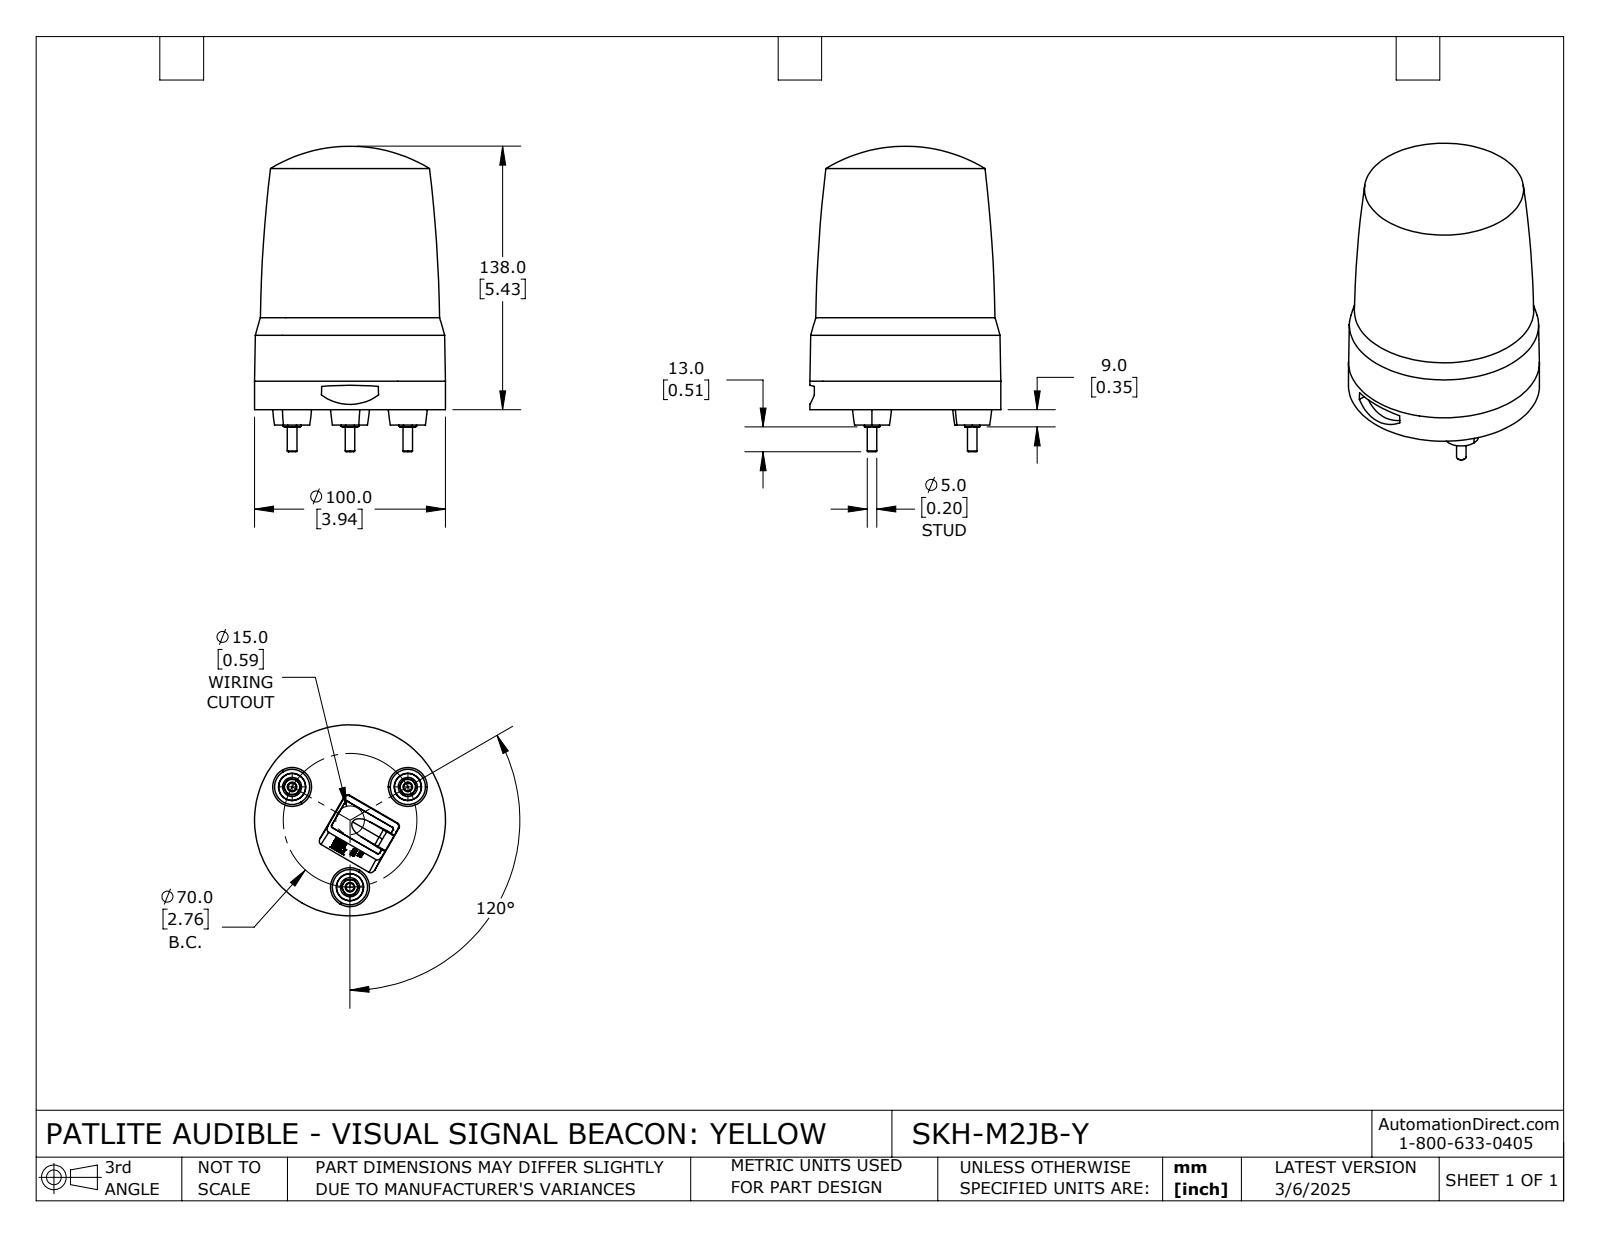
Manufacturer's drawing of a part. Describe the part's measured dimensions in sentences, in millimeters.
The part is named "SKH-M2JB-Y". Its 3-D file was written by "SolidWorks 2024 (CONFIG_CONTROL_DESIGN)". It is 1 solid with 446 faces: 211 planar, 22 cylindrical and 213 other. Overall it measures 160 by 100 by 100 millimeters. Its volume is 900 363 cubic millimeters and its surface area 55 433 square millimeters. Round bosses or shafts: 3 of diameter 10, 3 of diameter 5, 1 of diameter 100. Partial cylindrical surfaces (rounded edges, fillets, slot ends): 4 of radius 2, 2 of radius 5.05, 1 of radius 45, 1 of radius 80.12. The main face-to-face distances are 8, 14.85, 6.85, 1.6, 16.45, 8.45, 3.8, 4.2, 11.05, 12.65.
